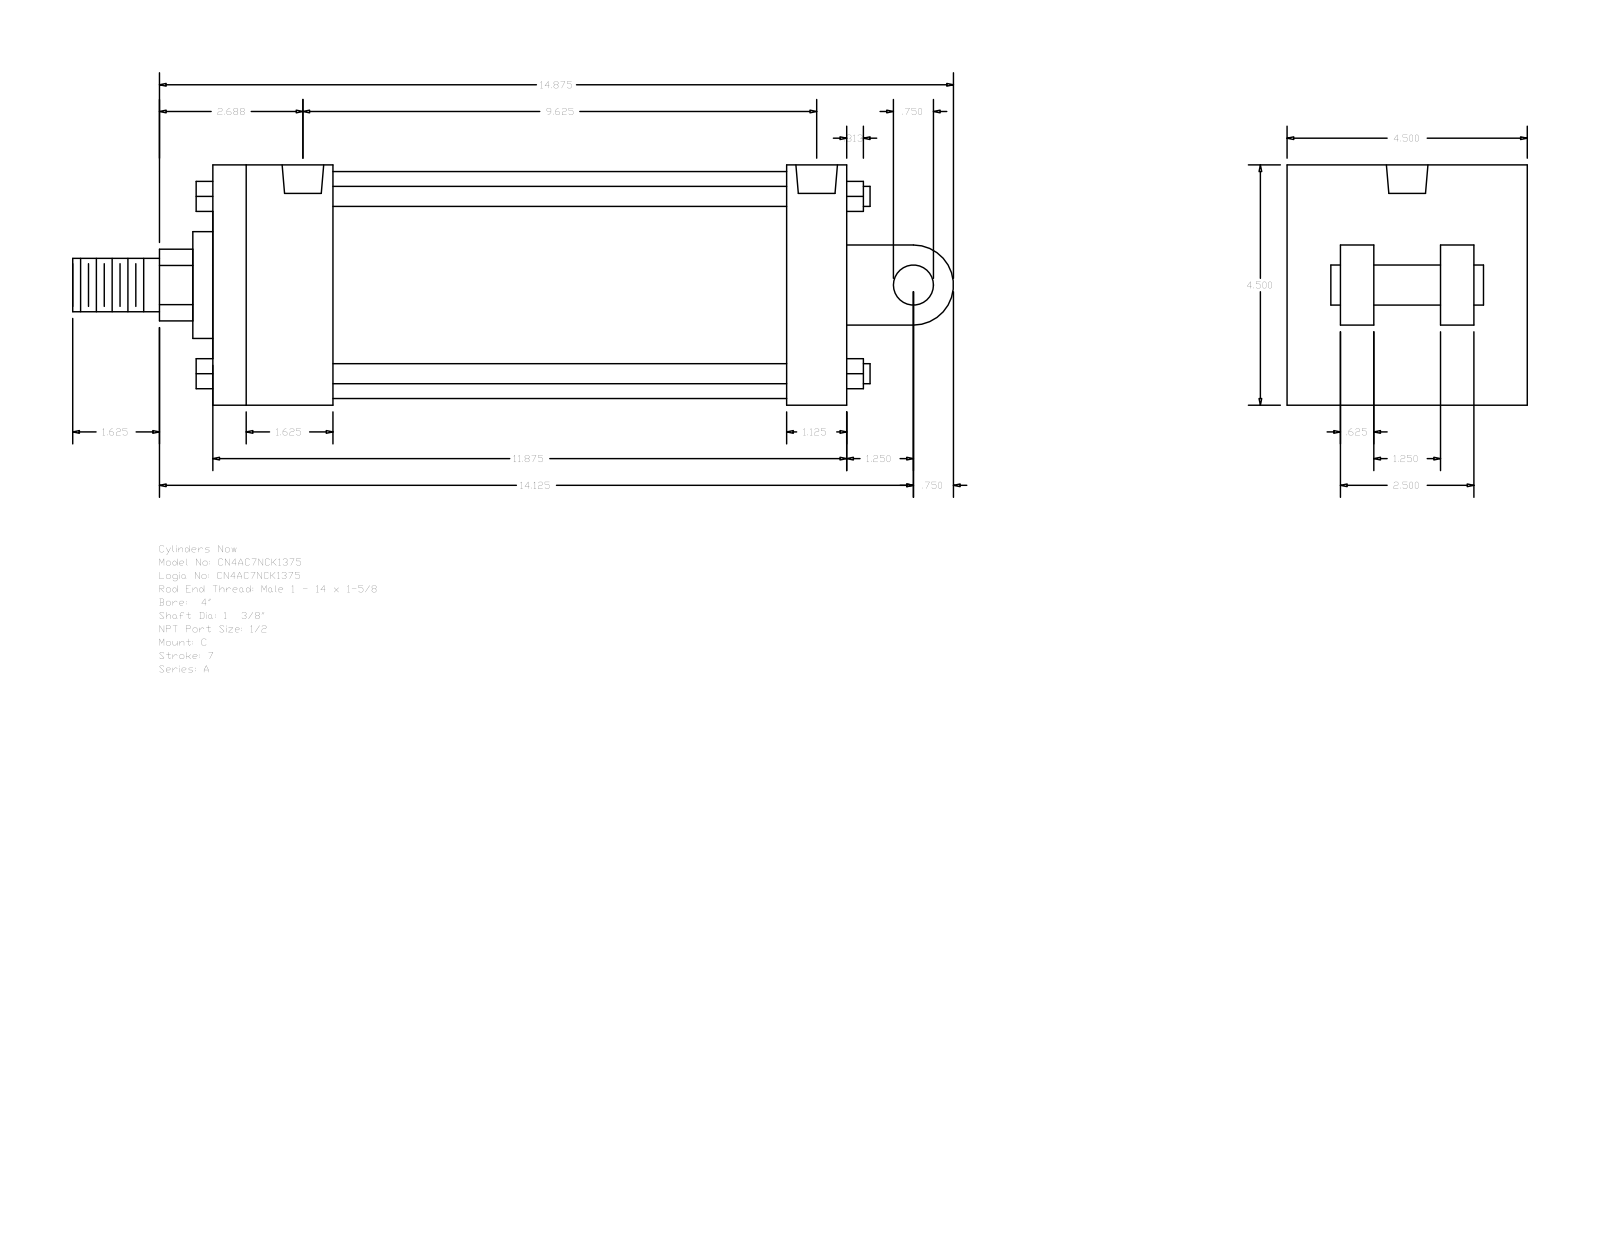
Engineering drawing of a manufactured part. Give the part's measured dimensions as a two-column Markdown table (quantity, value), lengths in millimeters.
| quantity | value |
| --- | --- |
| part name | A_C__0400_1.375 |
| STEP written by | GSSL Pune (CONFIG_CONTROL_DESIGN) |
| units | millimeters |
| bodies | 0 solids, 135 faces (102 planar, 33 cylindrical, 0 other) |
| overall size | 419.1 × 114.3 × 114.3 |
| round holes (diameter × count) | 8.73 × 4, 19.77 × 2 |
| round bosses / shafts (diameter × count) | 9.53 × 4, 107.95 × 1, 50.8 × 1, 34.92 × 1, 25.4 × 1, 19.05 × 1 |
| partial cylindrical surfaces (radius × count) | 17.06 × 1, 19.05 × 1 |
| main face-to-face distances | 114.3, 301.62, 57.15, 73.03, 273.05, 28.57, 215.9, 244.47, 41.27, 25.4 |
| hole center spacings | 3.18, 238.12, 241.3, 244.48 |
